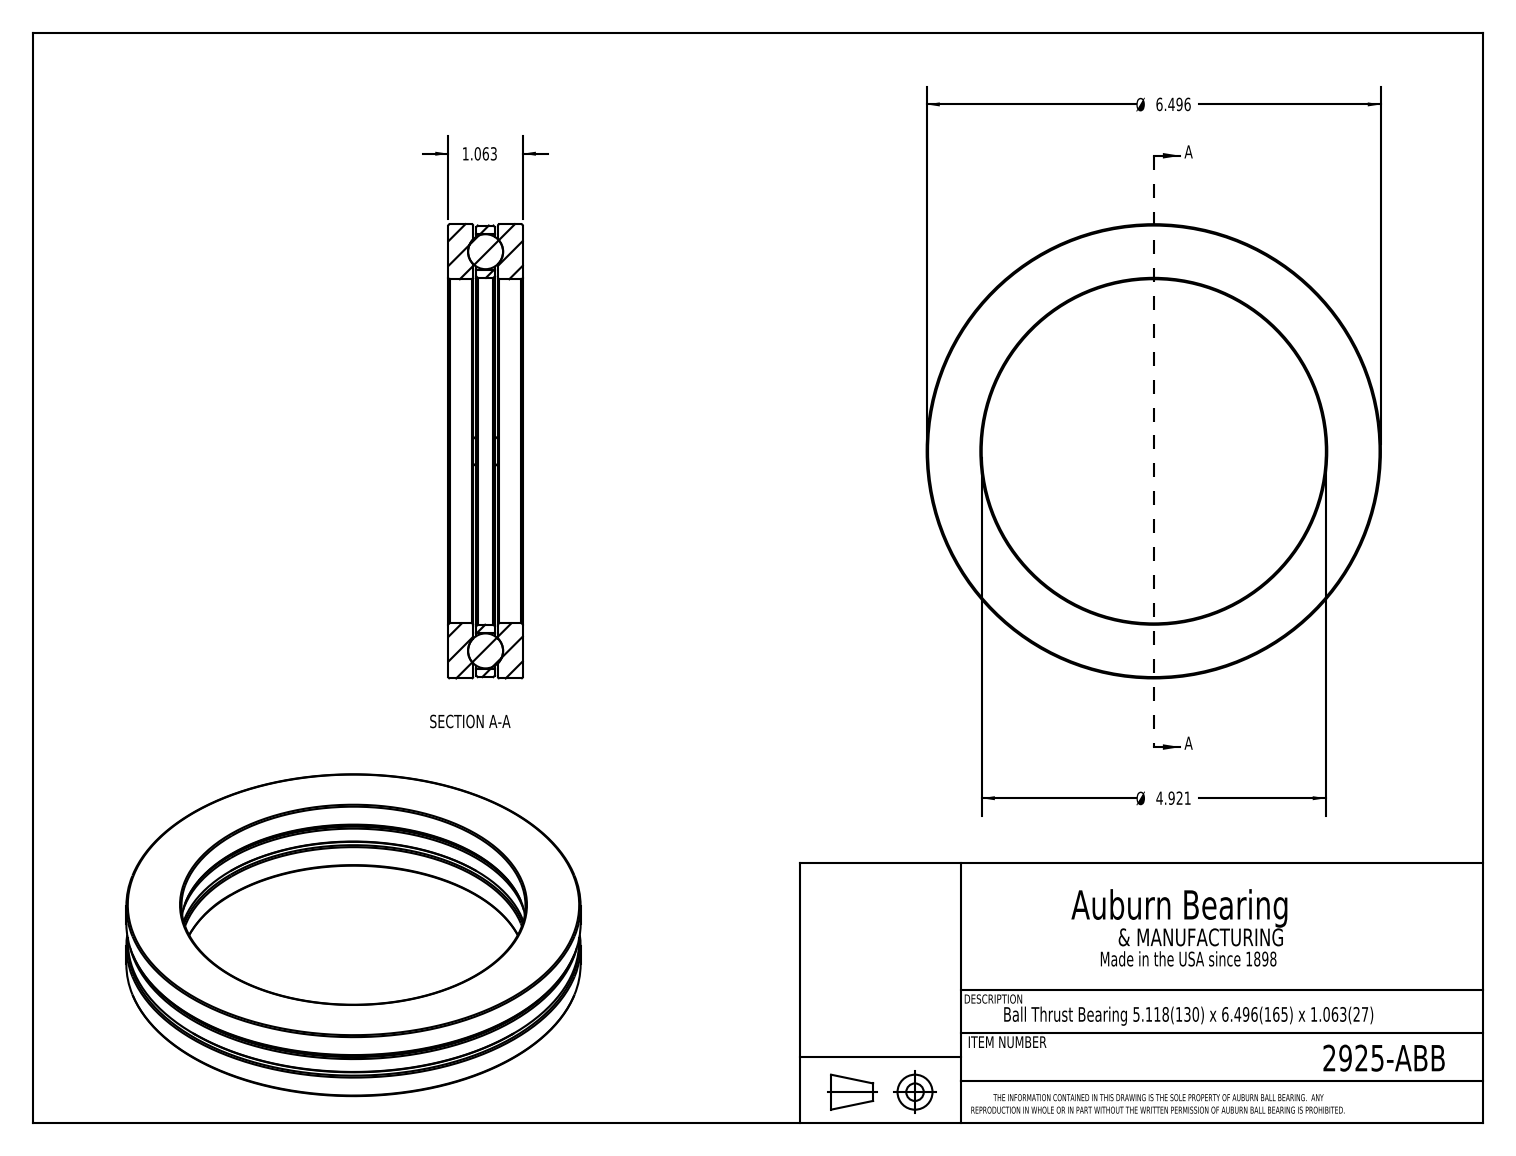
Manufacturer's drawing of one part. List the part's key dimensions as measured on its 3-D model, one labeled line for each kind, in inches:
Part name (STEP PRODUCT): 2925-ABB
STEP written by: SolidWorks 2017 (CONFIG_CONTROL_DESIGN)
Units: inches
Bodies: 7 solids, 36 faces (8 planar, 10 cylindrical, 18 other)
Overall size (bounding box): 6.496 × 6.496 × 1.063
Volume: 11.43 in³ · Surface area: 112 in²
Round holes (diameter × count): ⌀0.51 ×4, ⌀5.118 ×1, ⌀5.158 ×1
Round bosses / shafts (diameter × count): ⌀6.496 ×1, ⌀6.456 ×1
Main face-to-face distances: 0.398, 0.665, 0.354, 1.063, 0.709, 0.044, 0.31, 0.266
Hole centre spacings: 2.904, 4.106, 5.807
